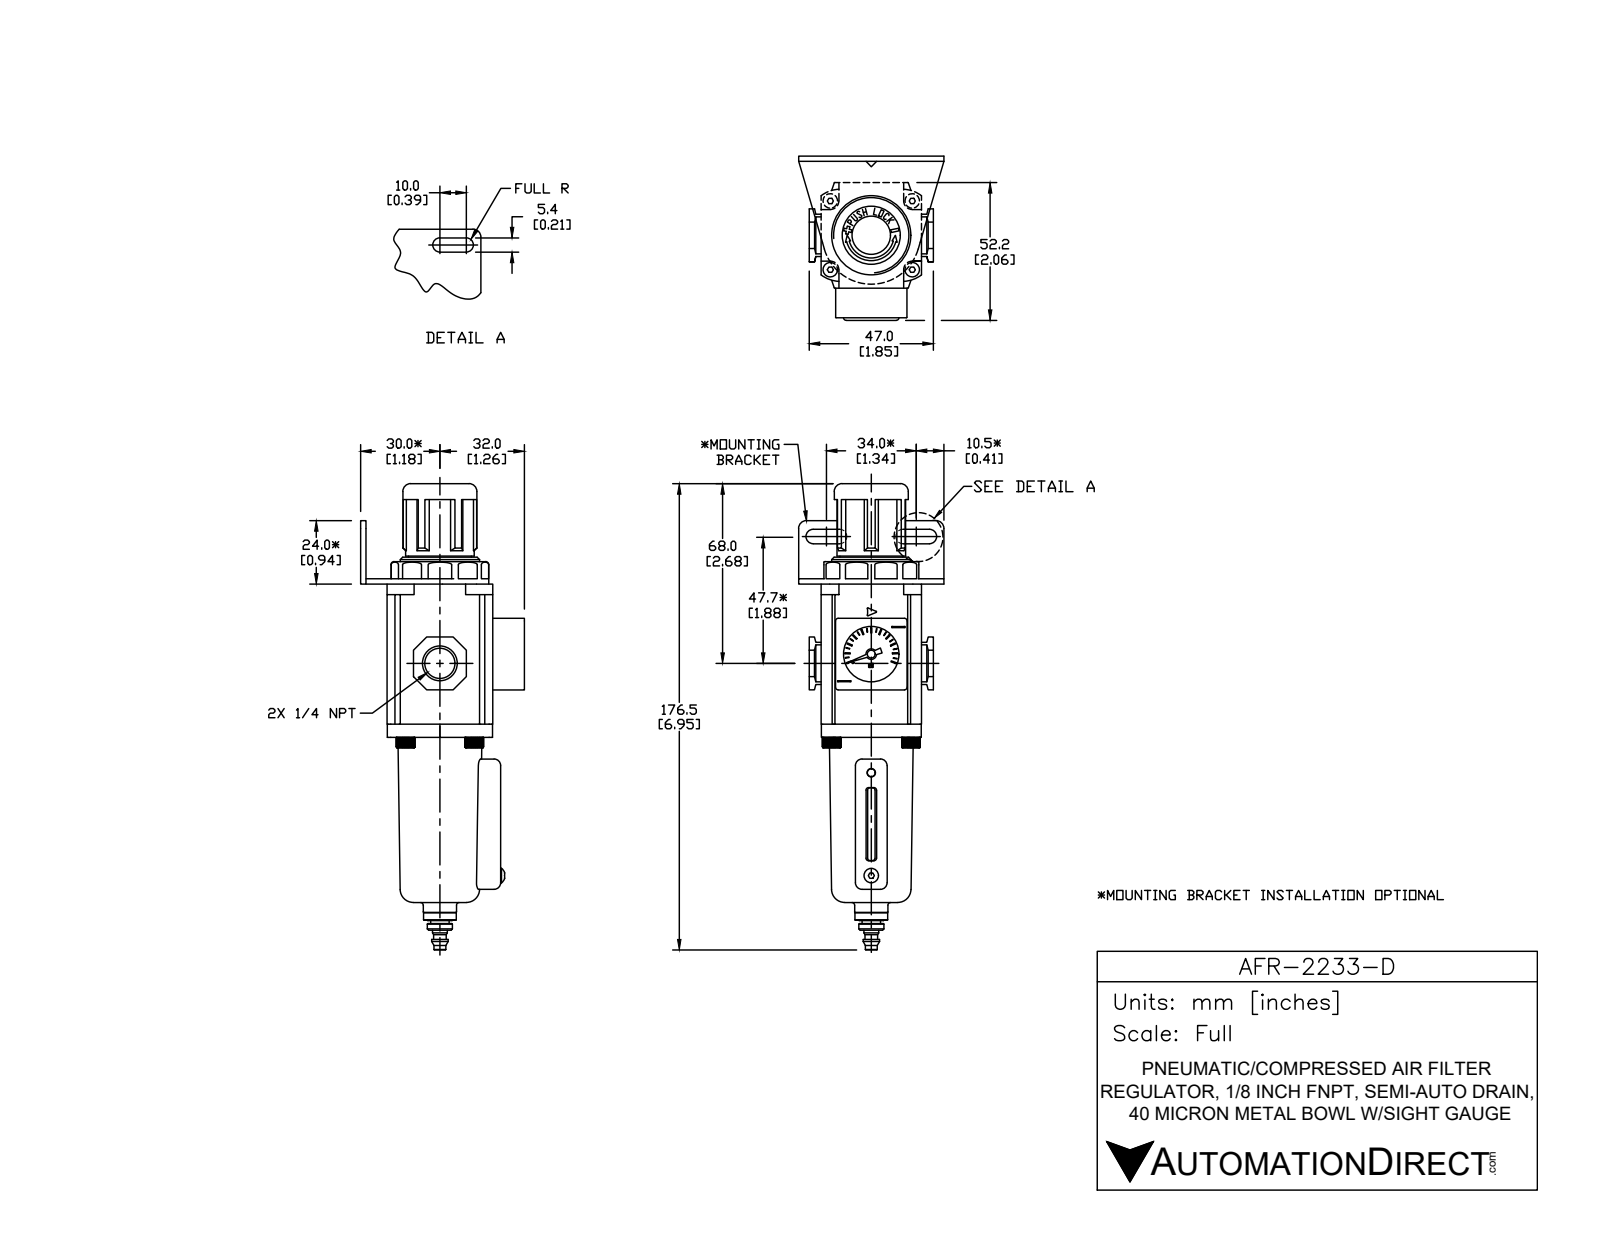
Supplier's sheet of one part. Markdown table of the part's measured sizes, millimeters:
| quantity | value |
| --- | --- |
| part name | AFR-2233-D |
| STEP written by | SolidWorks 2015 (CONFIG_CONTROL_DESIGN) |
| units | millimeters |
| bodies | 16 solids, 657 faces (397 planar, 190 cylindrical, 70 other) |
| overall size | 176.5 × 62 × 55 |
| volume | 168 168 mm³ |
| surface area | 43 405 mm² |
| round holes (diameter × count) | 3 × 7, 2 × 1, 11.13 × 1, 21 × 1, 22 × 1, 30 × 1 |
| round bosses / shafts (diameter × count) | 5.5 × 6, 7 × 4, 2.7 × 2, 28 × 1, 26 × 1, 23.8 × 1, 14 × 1, 12.6 × 1 |
| partial cylindrical surfaces (radius × count) | 1 × 16, 0.3 × 12, 1.2 × 10, 1.3 × 8, 2.5 × 8, 3.25 × 6, 0.5 × 4, 2.75 × 4 |
| main face-to-face distances | 2, 53, 55, 40, 38, 39, 1, 10, 50, 9 |
| hole center spacings | 20.23, 14.5, 26, 31, 40.46, 28.99 |
